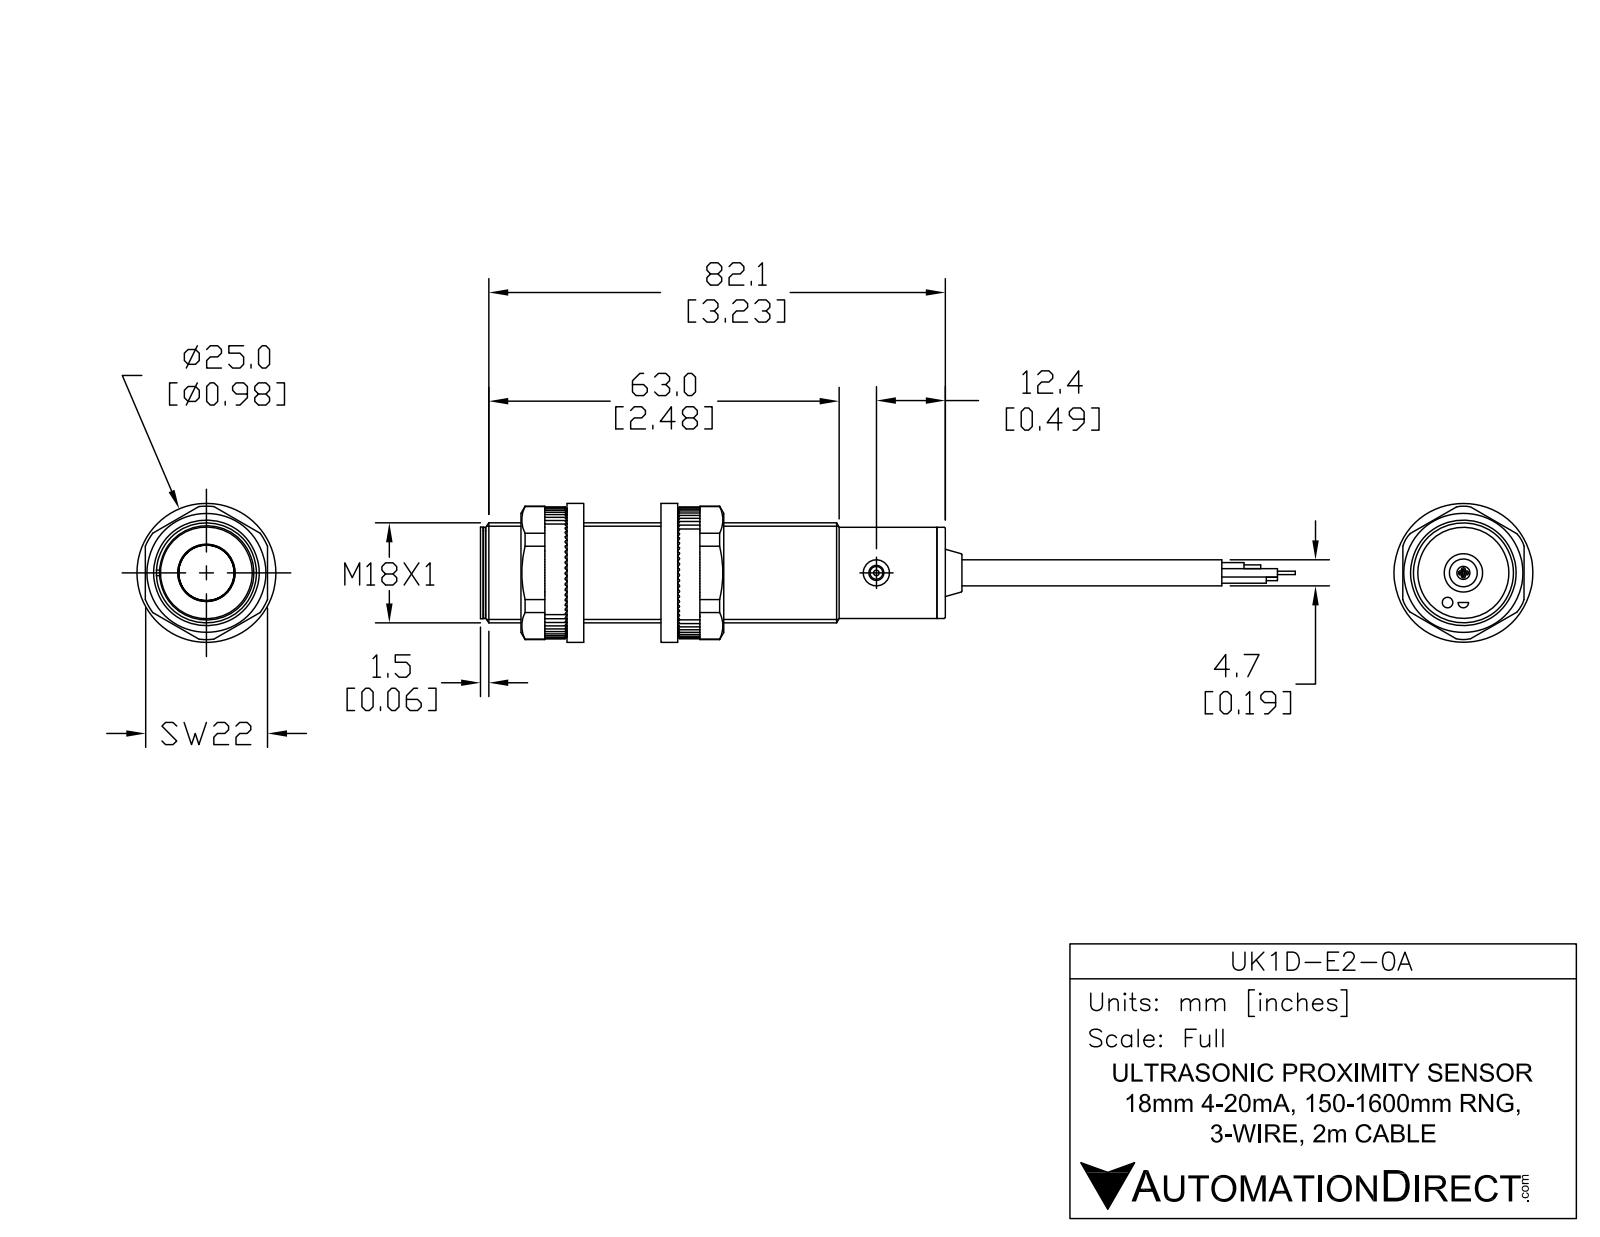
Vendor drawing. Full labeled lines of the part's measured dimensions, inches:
Part name (STEP PRODUCT): UK1D-E2-0A
STEP written by: SolidWorks 2017 (AUTOMOTIVE_DESIGN)
Units: inches
Bodies: 6 solids, 55 faces (17 planar, 24 cylindrical, 14 other)
Overall size (bounding box): 4.832 × 0.709 × 0.709
Volume: 1.285 in³ · Surface area: 10.69 in²
Round holes (diameter × count): ⌀0.185 ×2, ⌀0.106 ×1
Round bosses / shafts (diameter × count): ⌀0.709 ×1, ⌀0.646 ×1, ⌀0.622 ×1, ⌀0.374 ×1, ⌀0.189 ×1, ⌀0.091 ×1
Main face-to-face distances: 3.193, 3.252, 0.059, 0.039, 3.232, 3.291, 0.041, 3.234, 3.293, 3.257
